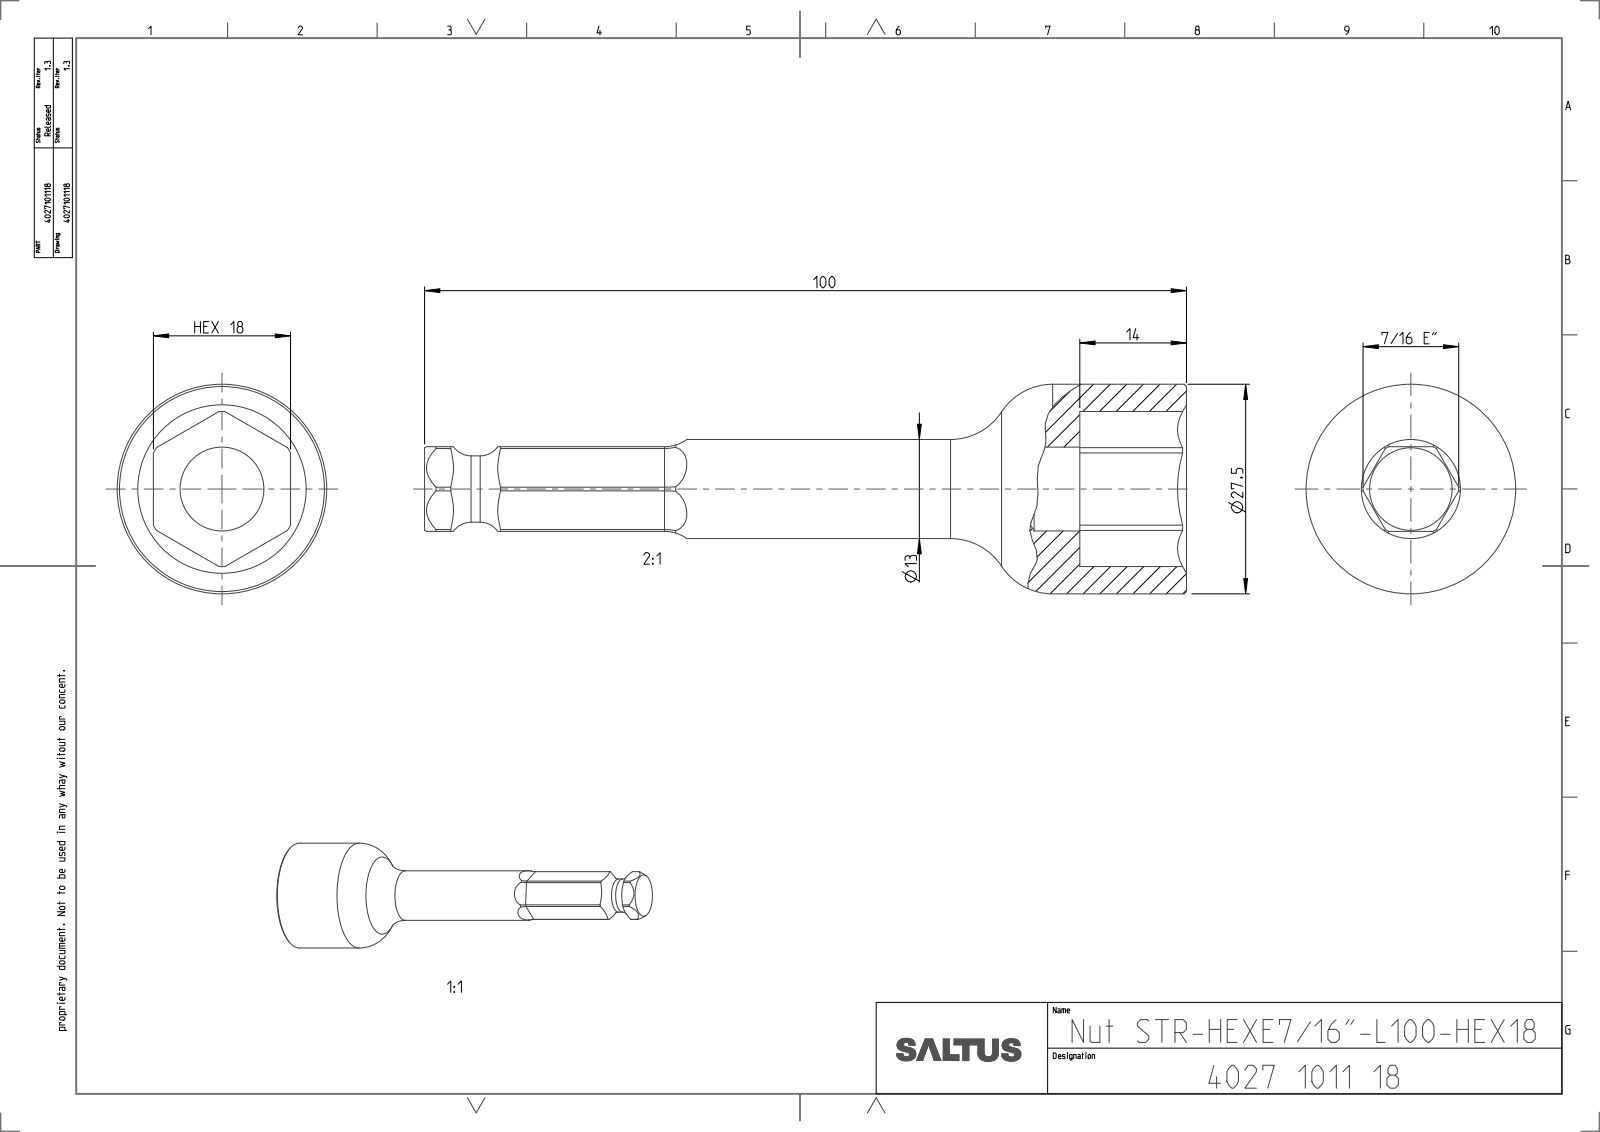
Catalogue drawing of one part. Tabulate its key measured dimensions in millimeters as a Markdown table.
| quantity | value |
| --- | --- |
| part name | 4027101118 |
| STEP written by | CREO PARAMETRIC BY PTC INC, 2022414 (CONFIG_CONTROL_DESIGN) |
| units | millimeters |
| bodies | 1 solid, 75 faces (21 planar, 32 cylindrical, 22 other) |
| overall size | 100 × 27.5 × 27.5 |
| volume | 18 481 mm³ |
| surface area | 6 961 mm² |
| round holes (diameter × count) | 11 × 1 |
| round bosses / shafts (diameter × count) | 27.5 × 1, 13 × 1, 8.7 × 1 |
| partial cylindrical surfaces (radius × count) | 5 × 6, 6.28 × 1, 10.17 × 1 |
| main face-to-face distances | 11.1, 18, 14, 86, 100 |
